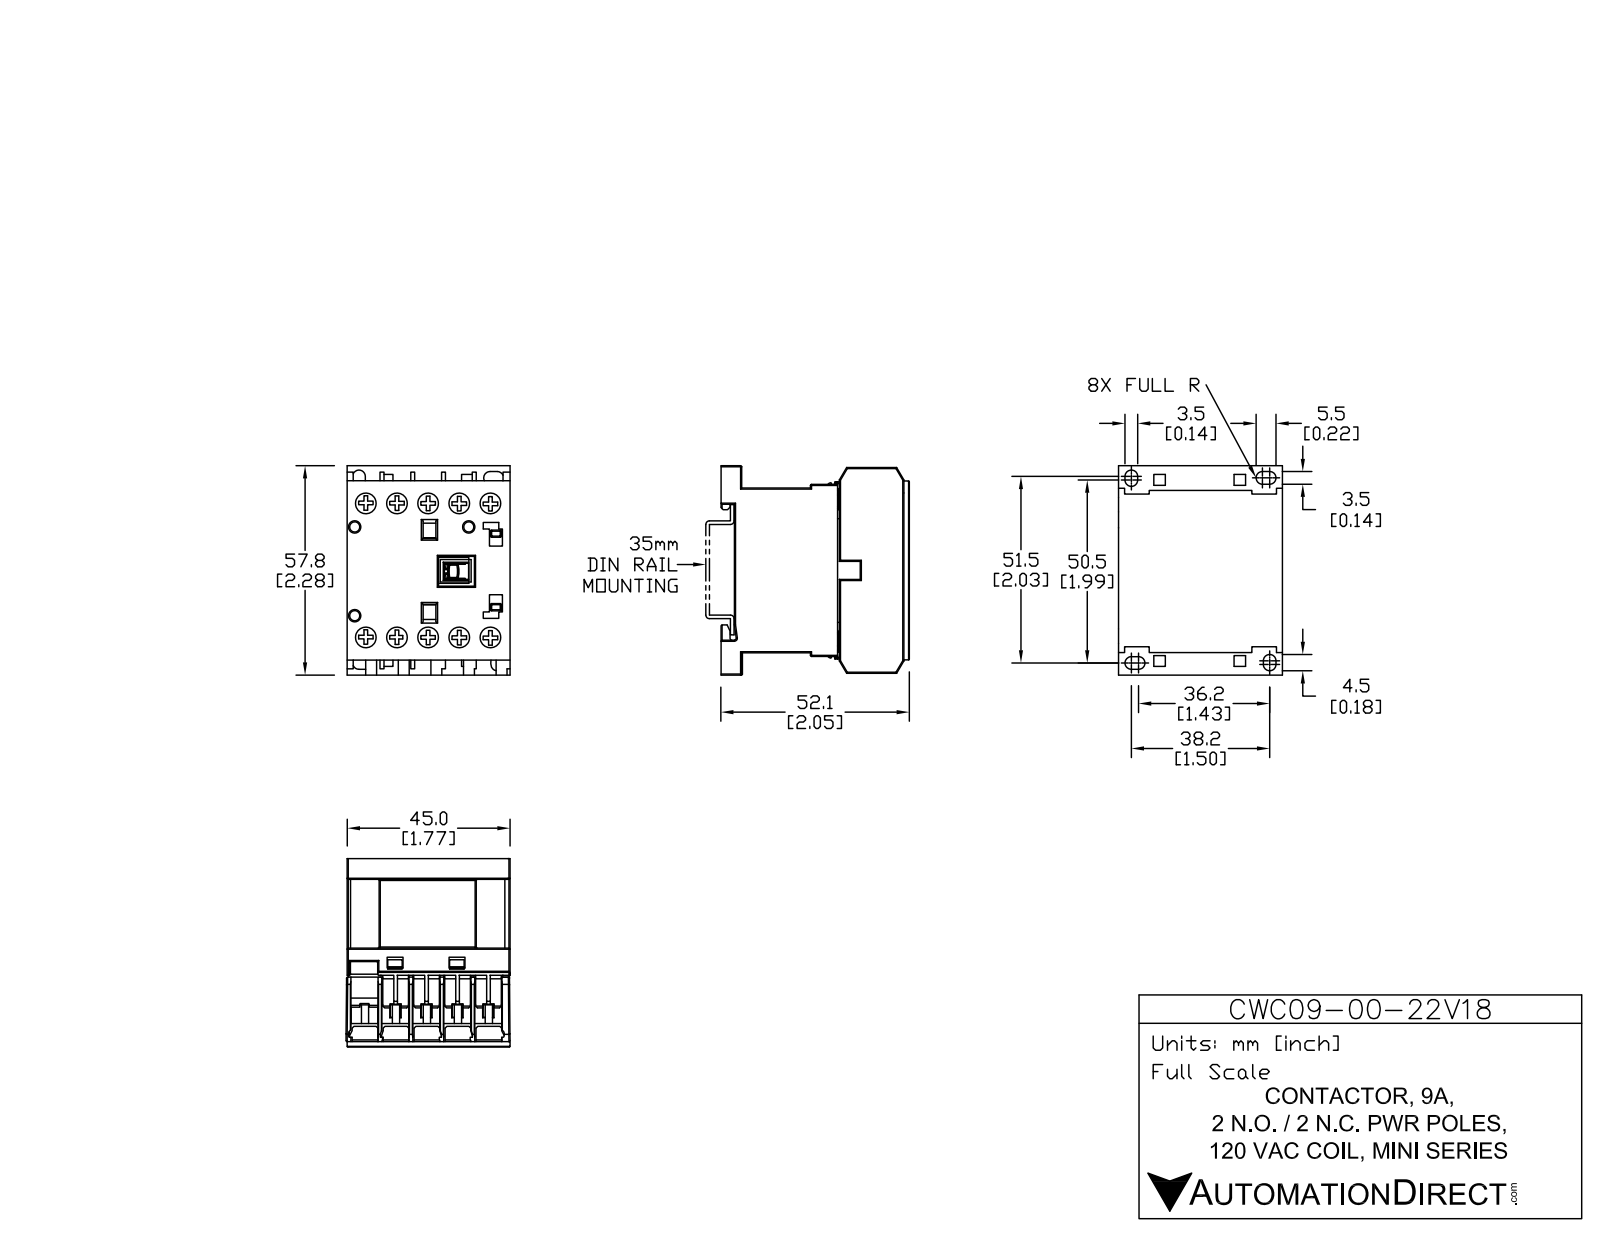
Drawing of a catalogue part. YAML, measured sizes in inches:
part_name: "CWC09-00-22V18"
step_written_by: "SolidWorks 2013 (AUTOMOTIVE_DESIGN)"
units: inches
bodies: {solids: 15, faces: 535, planar: 445, cylindrical: 90, other: 0}
overall_size: [2.285, 2.052, 1.801]
volume: 5.927
surface_area: 47.18
round_holes:
  - {diameter: 0.244, count: 10}
  - {diameter: 0.11, count: 3}
round_bosses_or_shafts:
  - {diameter: 0.232, count: 10}
partial_cylinders:
  - {radius: 0.012, count: 20}
  - {radius: 0.068, count: 6}
  - {radius: 0.068, count: 2}
  - {radius: 0.013, count: 1}
  - {radius: 0.017, count: 1}
  - {radius: 0.022, count: 1}
face_to_face_distances: [0.325, 1.791, 0.049, 0.65, 0.374, 0.217, 0.699, 0.202, 0.419, 0.276]
hole_center_spacings: [0.337, 1.494, 0.673, 1.603, 1.455, 1.01, 1.771, 0.272]
